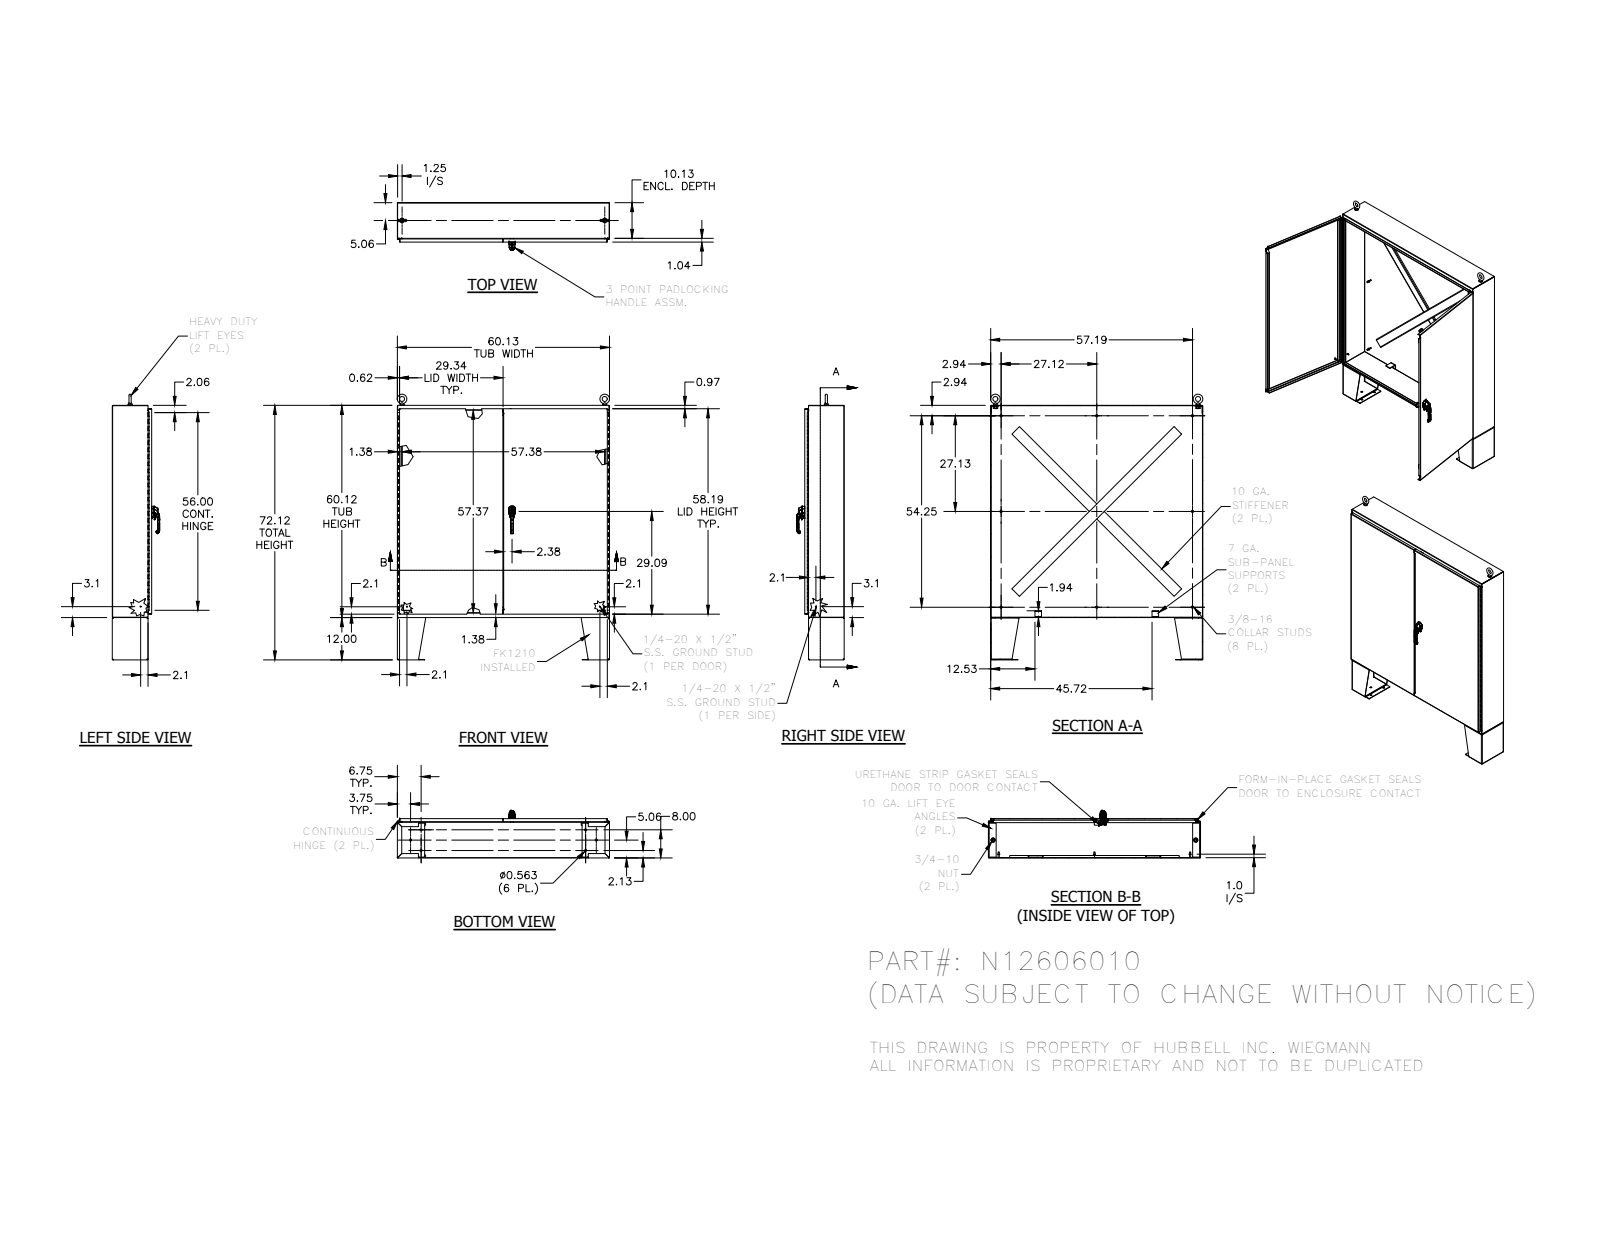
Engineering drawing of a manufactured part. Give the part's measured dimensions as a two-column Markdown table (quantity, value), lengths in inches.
| quantity | value |
| --- | --- |
| part name | N12606010 |
| STEP written by | SolidWorks 2018 (AUTOMOTIVE_DESIGN) |
| units | inches |
| bodies | 76 solids, 2392 faces (1384 planar, 708 cylindrical, 300 other) |
| overall size | 75.248 × 62.21 × 13.338 |
| volume | 1 247 in³ |
| surface area | 24 996 in² |
| round holes (diameter × count) | 0.563 × 18, 0.277 × 8, 0.2 × 4, 0.28 × 3, 0.125 × 2, 0.125 × 2, 0.241 × 2, 0.25 × 2, 0.252 × 2, 0.4 × 2, 0.45 × 2, 0.642 × 2 |
| round bosses / shafts (diameter × count) | 0.33 × 8, 0.25 × 5, 0.625 × 4, 0.625 × 4, 0.337 × 3, 1.25 × 2, 1.12 × 2, 1 × 2 |
| partial cylindrical surfaces (radius × count) | 0.031 × 24, 0.094 × 23, 0.219 × 22, 0.05 × 18, 0.025 × 16, 0.125 × 15, 0.03 × 13, 0.067 × 8 |
| main face-to-face distances | 0.094, 11.067, 10.973, 11.16, 60.031, 60.125, 59.938, 0.125, 0.125, 10.031 |
| hole center spacings | 2.041, 4.198, 5, 6.153, 7.151, 8.75, 10.078, 46.398 |
